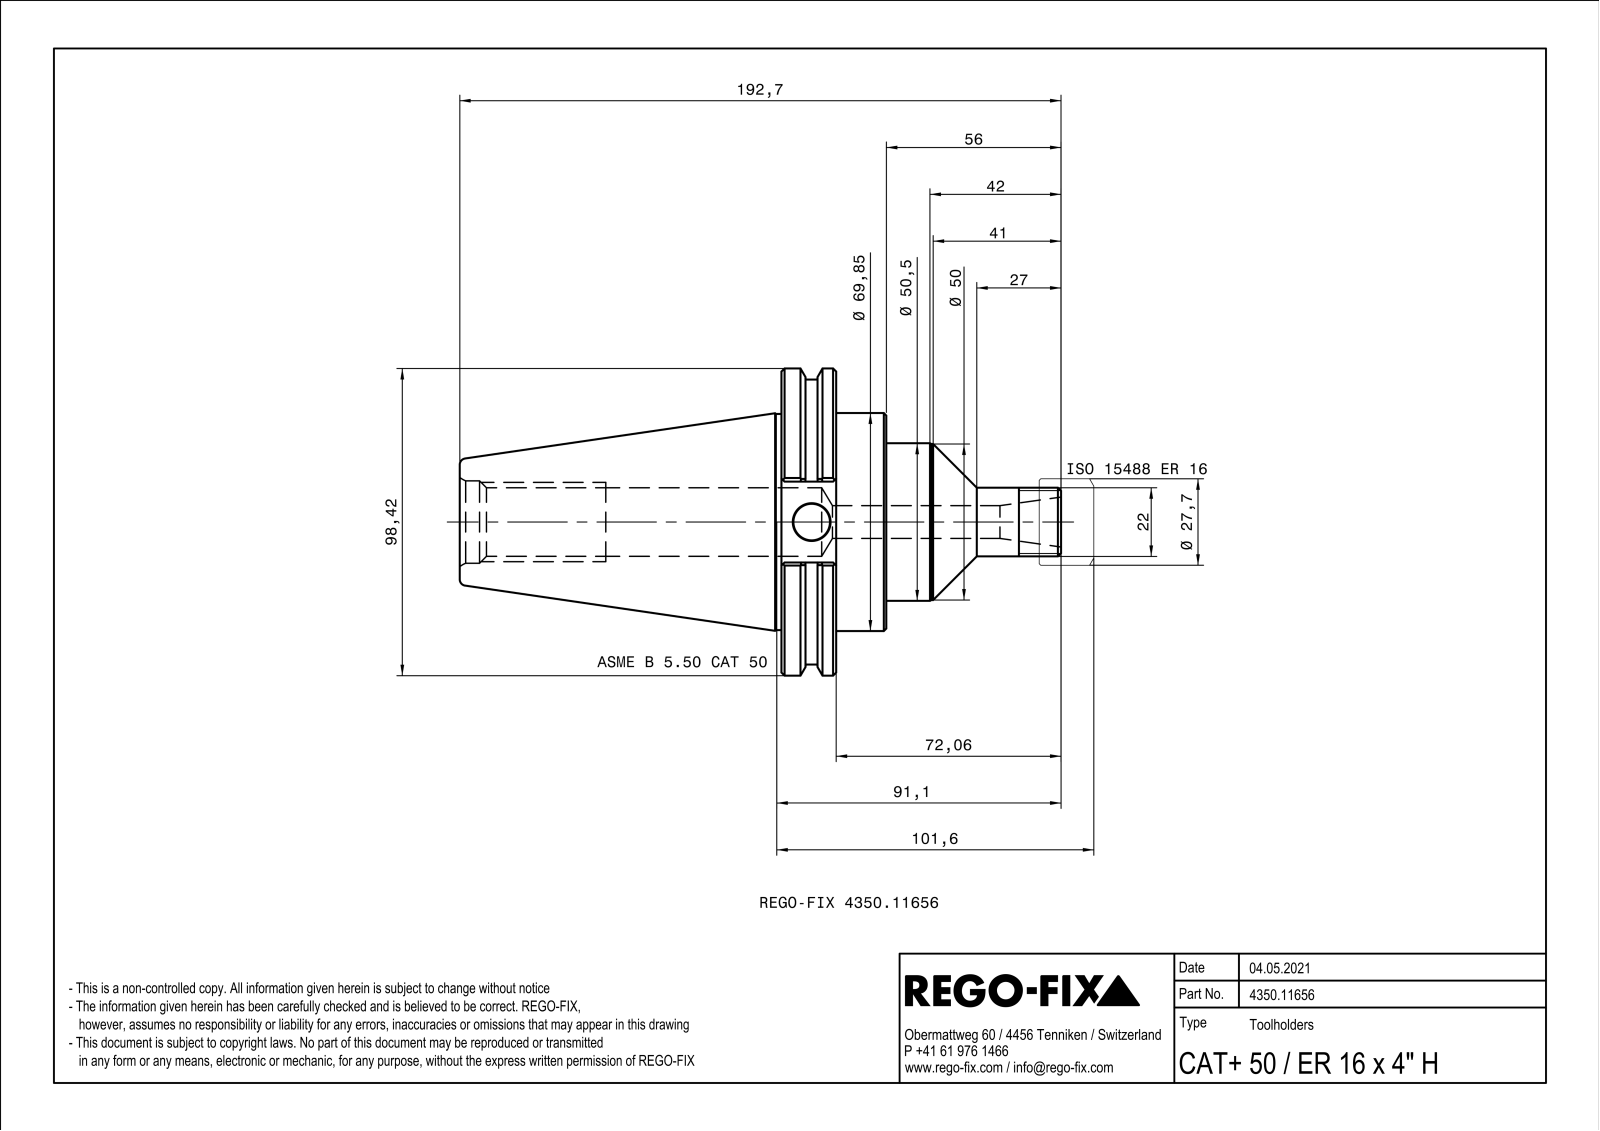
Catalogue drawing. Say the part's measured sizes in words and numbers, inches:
The part is named "NOCUT". Its 3-D file was written by "SIEMENS PLM Software Solid Edge ST10 (AUTOMOTIVE_DESIGN)". It is 2 solids with 248 faces: 102 planar, 59 cylindrical and 87 other. Overall it measures 7.602 by 3.887 by 3.726 inches. Its volume is 52.11 cubic inches and its surface area 176.8 square inches. Round holes: 2 of diameter 0.154, 2 of diameter 0.177, 1 of diameter 0.128, 1 of diameter 0.413, 1 of diameter 0.472, 1 of diameter 0.865, 1 of diameter 1.028, 1 of diameter 1.039. Round bosses or shafts: 1 of diameter 3.887, 1 of diameter 3.875, 1 of diameter 3.594, 1 of diameter 2.762, 1 of diameter 2.75, 1 of diameter 2.726, 1 of diameter 2, 1 of diameter 1.988. Partial cylindrical surfaces (rounded edges, fillets, slot ends): 4 of radius 0.02. The main face-to-face distances are 1.329, 0.691, 0.699, 0.63, 1.321, 0.638, 1.337, 5.388, 4.059, 2.863.
